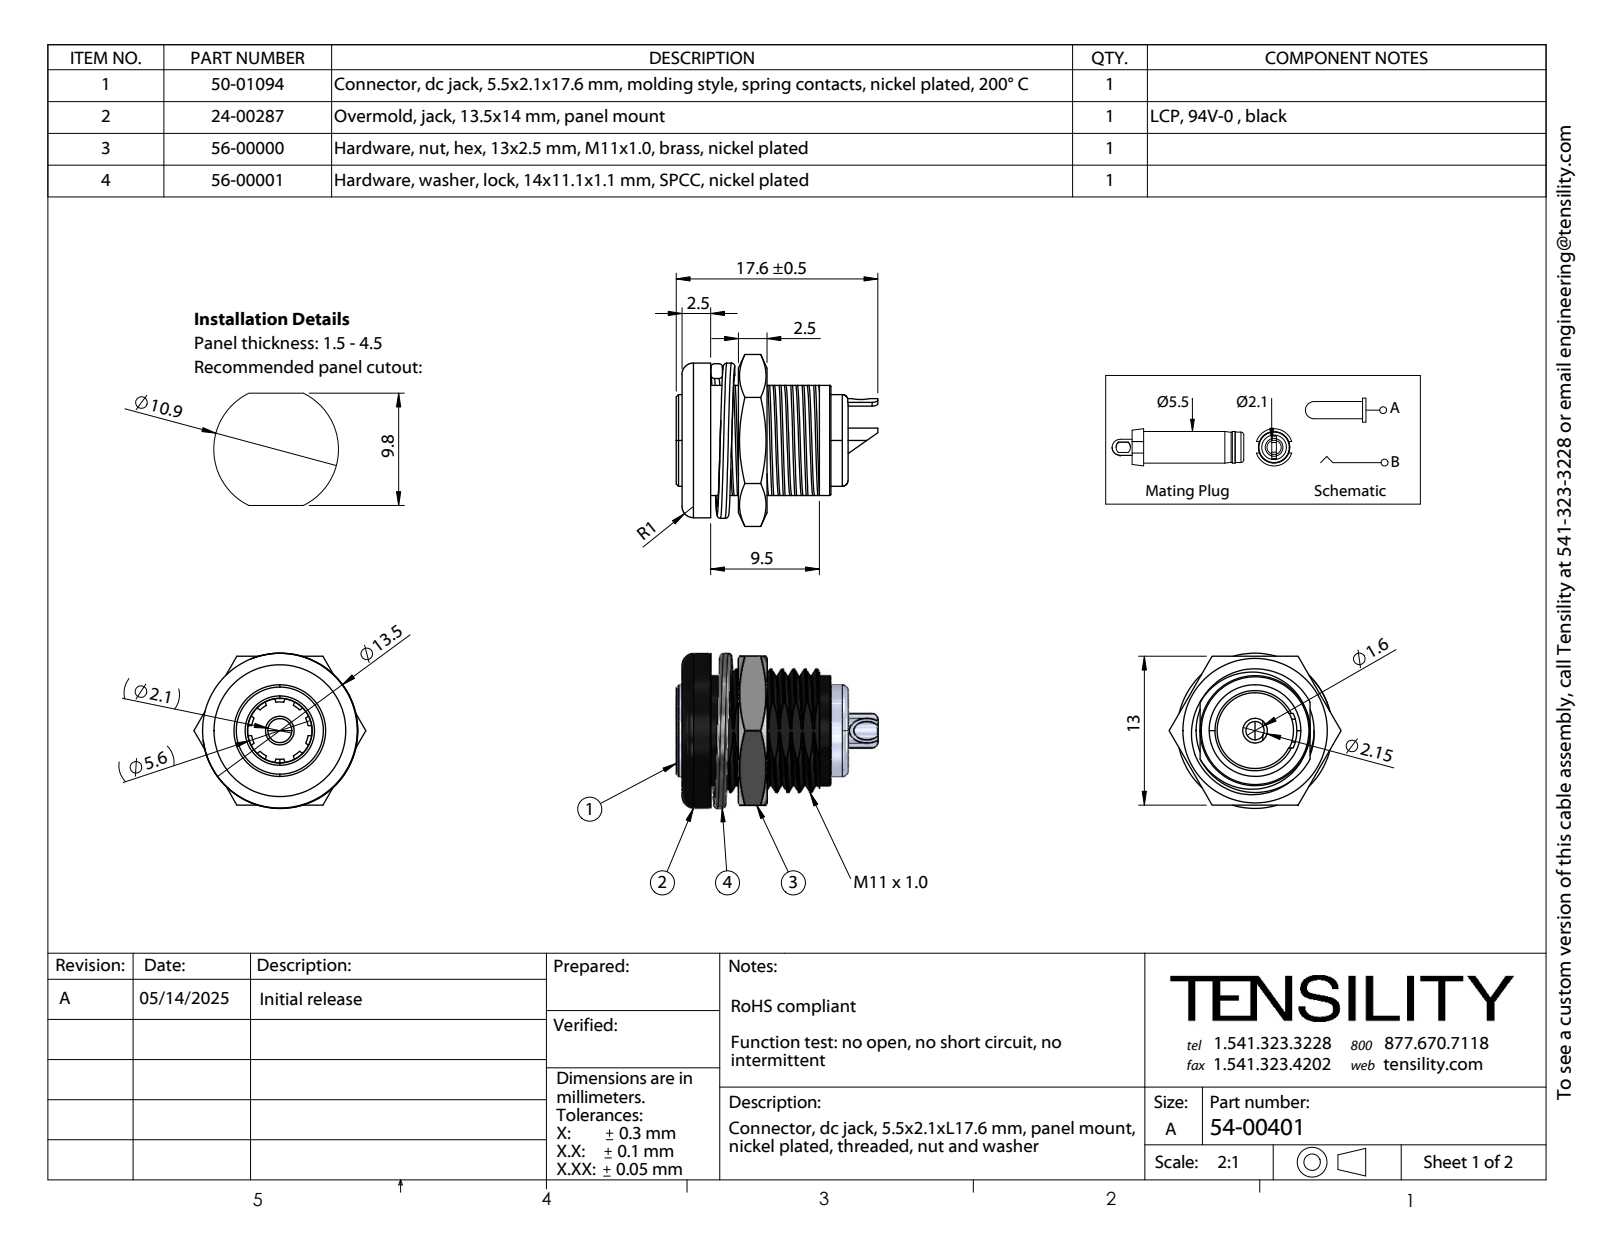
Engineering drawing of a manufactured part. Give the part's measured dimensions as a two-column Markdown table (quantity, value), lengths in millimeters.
| quantity | value |
| --- | --- |
| part name | 50-01012 insulator_Insulator; 50-01012 shell_Shell; 50-01012 center pin_Center pin; 54-00401_revA (+5 more) |
| STEP written by | SolidWorks 2021 (CONFIG_CONTROL_DESIGN) |
| units | millimeters |
| bodies | 7 solids, 295 faces (89 planar, 87 cylindrical, 119 other) |
| overall size | 17.6 × 15.01 × 13.55 |
| volume | 1 151 mm³ |
| surface area | 2 964 mm² |
| round holes (diameter × count) | 1.5 × 2, 1.6 × 1, 2.15 × 1, 2.5 × 1, 5.6 × 1, 5.65 × 1, 6.4 × 1, 6.6 × 1, 7.6 × 1, 8 × 1, 10.3 × 1 |
| round bosses / shafts (diameter × count) | 13.5 × 1, 9.6 × 1, 7.3 × 1, 6.2 × 1, 2.1 × 1 |
| partial cylindrical surfaces (radius × count) | 0.5 × 2, 3.35 × 1, 5.4 × 1 |
| main face-to-face distances | 2.5, 4.93, 13, 8.5, 11, 1, 7.43, 3.57, 2.43, 6.07 |
